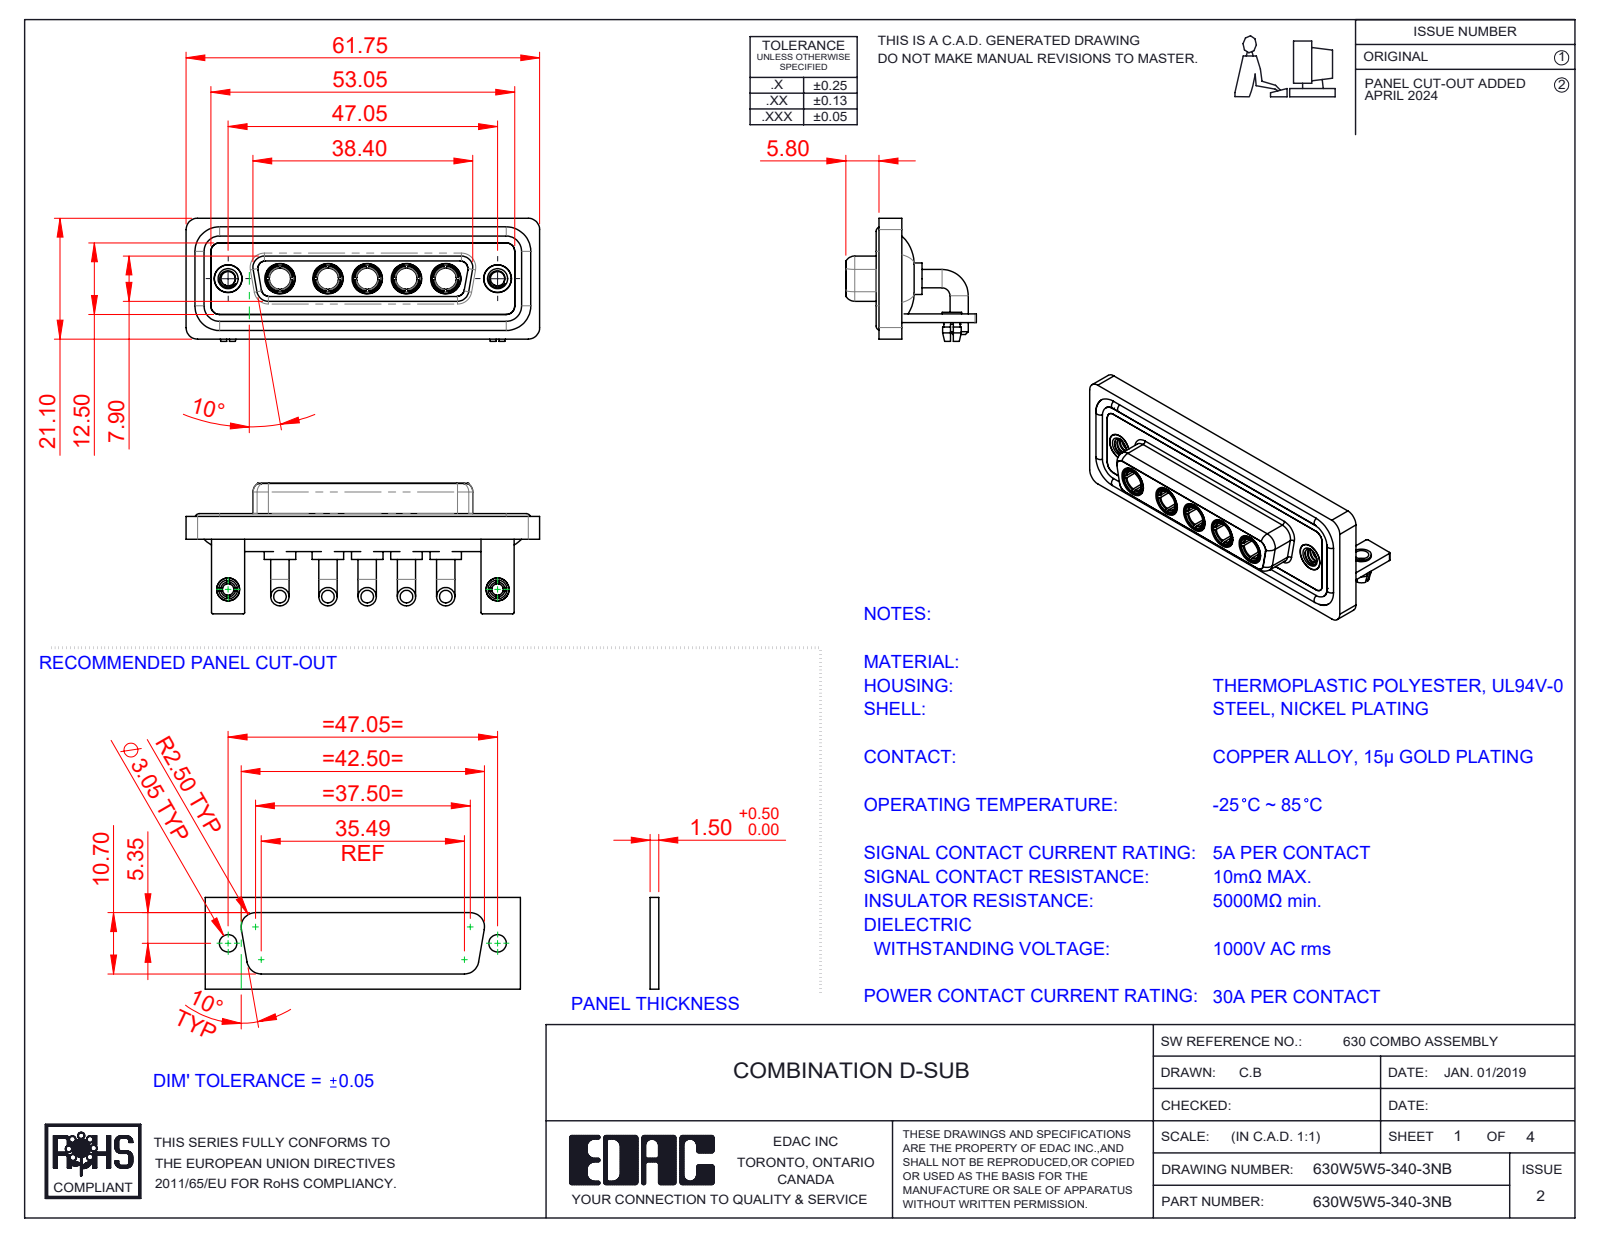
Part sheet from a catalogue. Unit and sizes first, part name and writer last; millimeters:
Units: millimetres
Overall size (bounding box): 61.75 × 22.8 × 21.5
Round holes (diameter × count): ⌀4.85 ×7, ⌀3.7 ×5, ⌀5.3 ×5, ⌀2.5 ×4, ⌀2 ×2, ⌀3.2 ×2, ⌀4 ×2, ⌀4.05 ×2, ⌀5 ×2
Round bosses / shafts (diameter × count): ⌀3.2 ×10, ⌀5.5 ×5, ⌀5.2 ×5, ⌀4.96 ×5, ⌀4.75 ×5, ⌀3.75 ×5, ⌀1.6 ×4, ⌀4.95 ×2
Partial cylindrical surfaces — rounded edges, fillets, slot ends (radius × count): R2 ×19, R1.5 ×18, R0.25 ×16, R1.35 ×8, R1.6 ×8, R0.5 ×5, R2.1 ×5, R0.6 ×4
Main face-to-face distances: 0.4, 1.8, 2.9, 3.7, 1.5, 4.1, 1.1, 1.4, 1.6, 2.5
Hole centre spacings: 6.86, 9.04, 38.01, 47.05, 6.87, 8.38, 13.72, 13.73
Volume: 8 971 mm³ · Surface area: 14 854 mm²
Bodies: 21 solids, 910 faces (318 planar, 367 cylindrical, 225 other)
Part name (STEP PRODUCT): 630Combo Stabilizer Bracket_50 Contacts; 630Combo Board Lock_50 Contacts; 630W5W5-340-3NB; 630Combo Housing_5W5 (+5 more)
STEP written by: SolidWorks 2023 (CONFIG_CONTROL_DESIGN)
